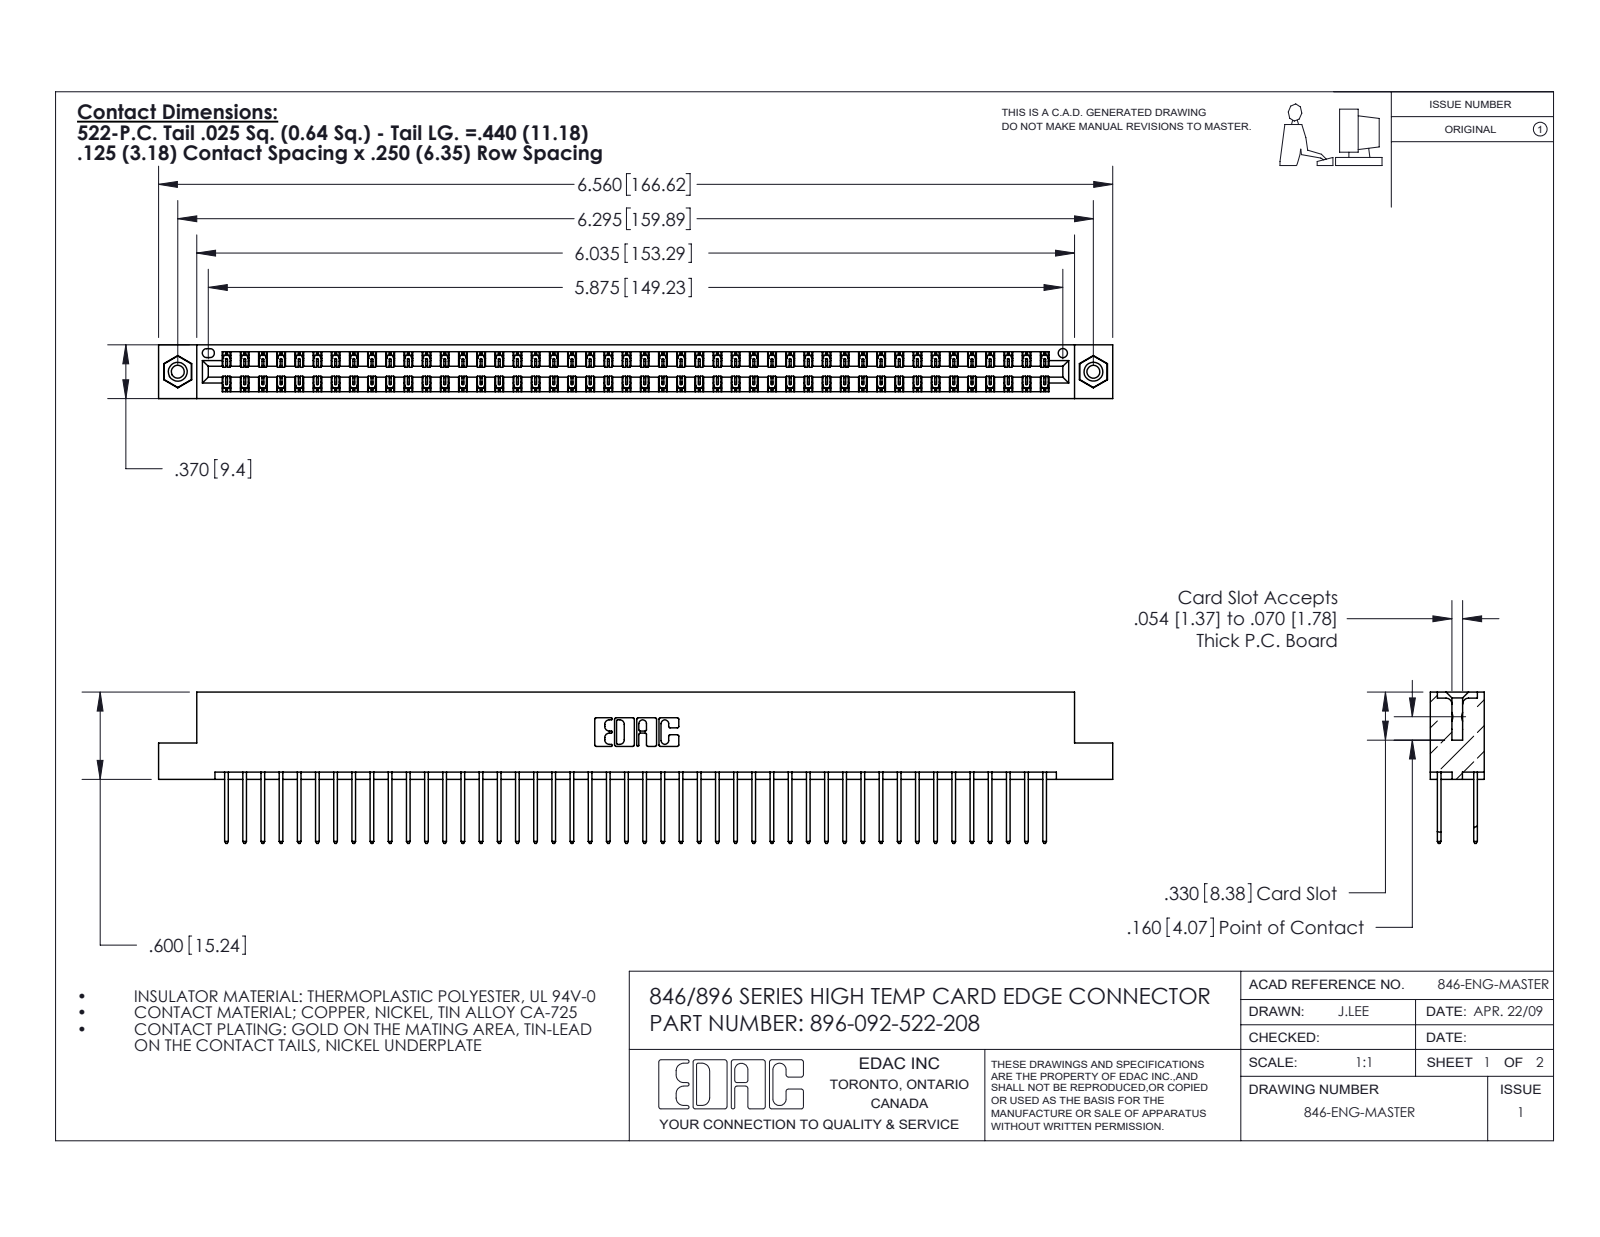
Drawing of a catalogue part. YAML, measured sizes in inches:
part_name: "346 Part_Flush Mounting Lugs - 0.156 Dia-TI; 396-092-522-208; 345-250-001_345-250-003-102; 345-292-001_345-293-122"
step_written_by: "SolidWorks 2016 (CONFIG_CONTROL_DESIGN)"
units: inches
bodies: {solids: 95, faces: 4966, planar: 3328, cylindrical: 1622, other: 16}
overall_size: [6.56, 1.04, 0.37]
volume: 1.007
surface_area: 36.99
round_holes:
  - {diameter: 0.089, count: 2}
  - {diameter: 0.125, count: 2}
  - {diameter: 0.156, count: 2}
  - {diameter: 0.064, count: 1}
round_bosses_or_shafts:
  - {diameter: 0.155, count: 2}
partial_cylinders:
  - {radius: 0.006, count: 138}
  - {radius: 0.01, count: 92}
  - {radius: 0.01, count: 22}
  - {radius: 0.007, count: 6}
  - {radius: 0.031, count: 6}
  - {radius: 0.026, count: 3}
  - {radius: 0.014, count: 2}
  - {radius: 0.022, count: 2}
face_to_face_distances: [0.048, 0.322, 0.25, 0.37, 0.072, 0.298, 0.025, 0.275, 0.148, 0.222]
hole_center_spacings: [0.246, 6.086, 6.295]
